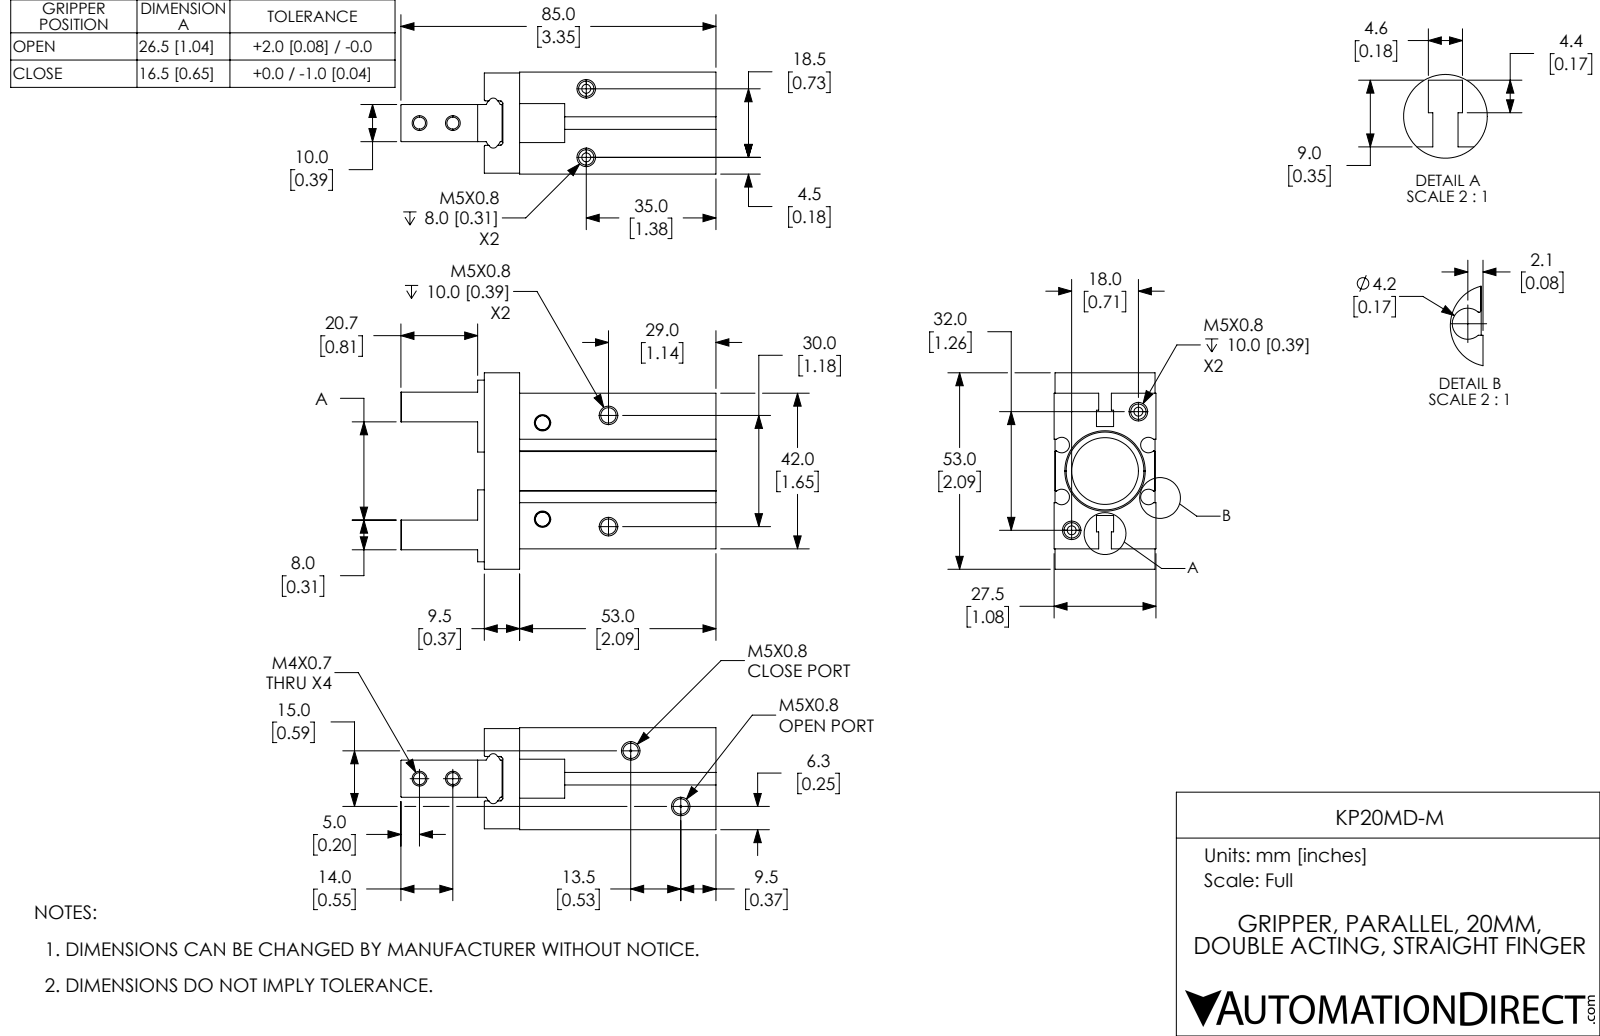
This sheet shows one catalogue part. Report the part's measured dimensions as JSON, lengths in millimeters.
{"part_name": "KP20MD-M-3; KP20MD-M-2; KP20MD-M-1; KP20MD-M", "step_written_by": "SolidWorks 2017 (CONFIG_CONTROL_DESIGN)", "units": "millimeters", "bodies": {"solids": 3, "faces": 246, "planar": 120, "cylindrical": 64, "other": 62}, "overall_size": [85, 53, 27.5], "volume_mm3": 63534, "surface_area_mm2": 21899, "round_holes": [[4.13, 8], [0.5, 2], [3.24, 2], [5.02, 2], [18, 1], [21, 1]], "partial_cylinders_radius": [[0.2, 8], [1.25, 4], [2.1, 4], [0.5, 2]], "face_to_face_distances": [8.5, 18.75, 27.5, 42, 27.2, 18.7, 19, 8.2, 27.25, 8.25], "hole_center_spacings": [18.36, 37.17, 45.94, 9, 12.13, 18.5, 20.18, 20.6]}
